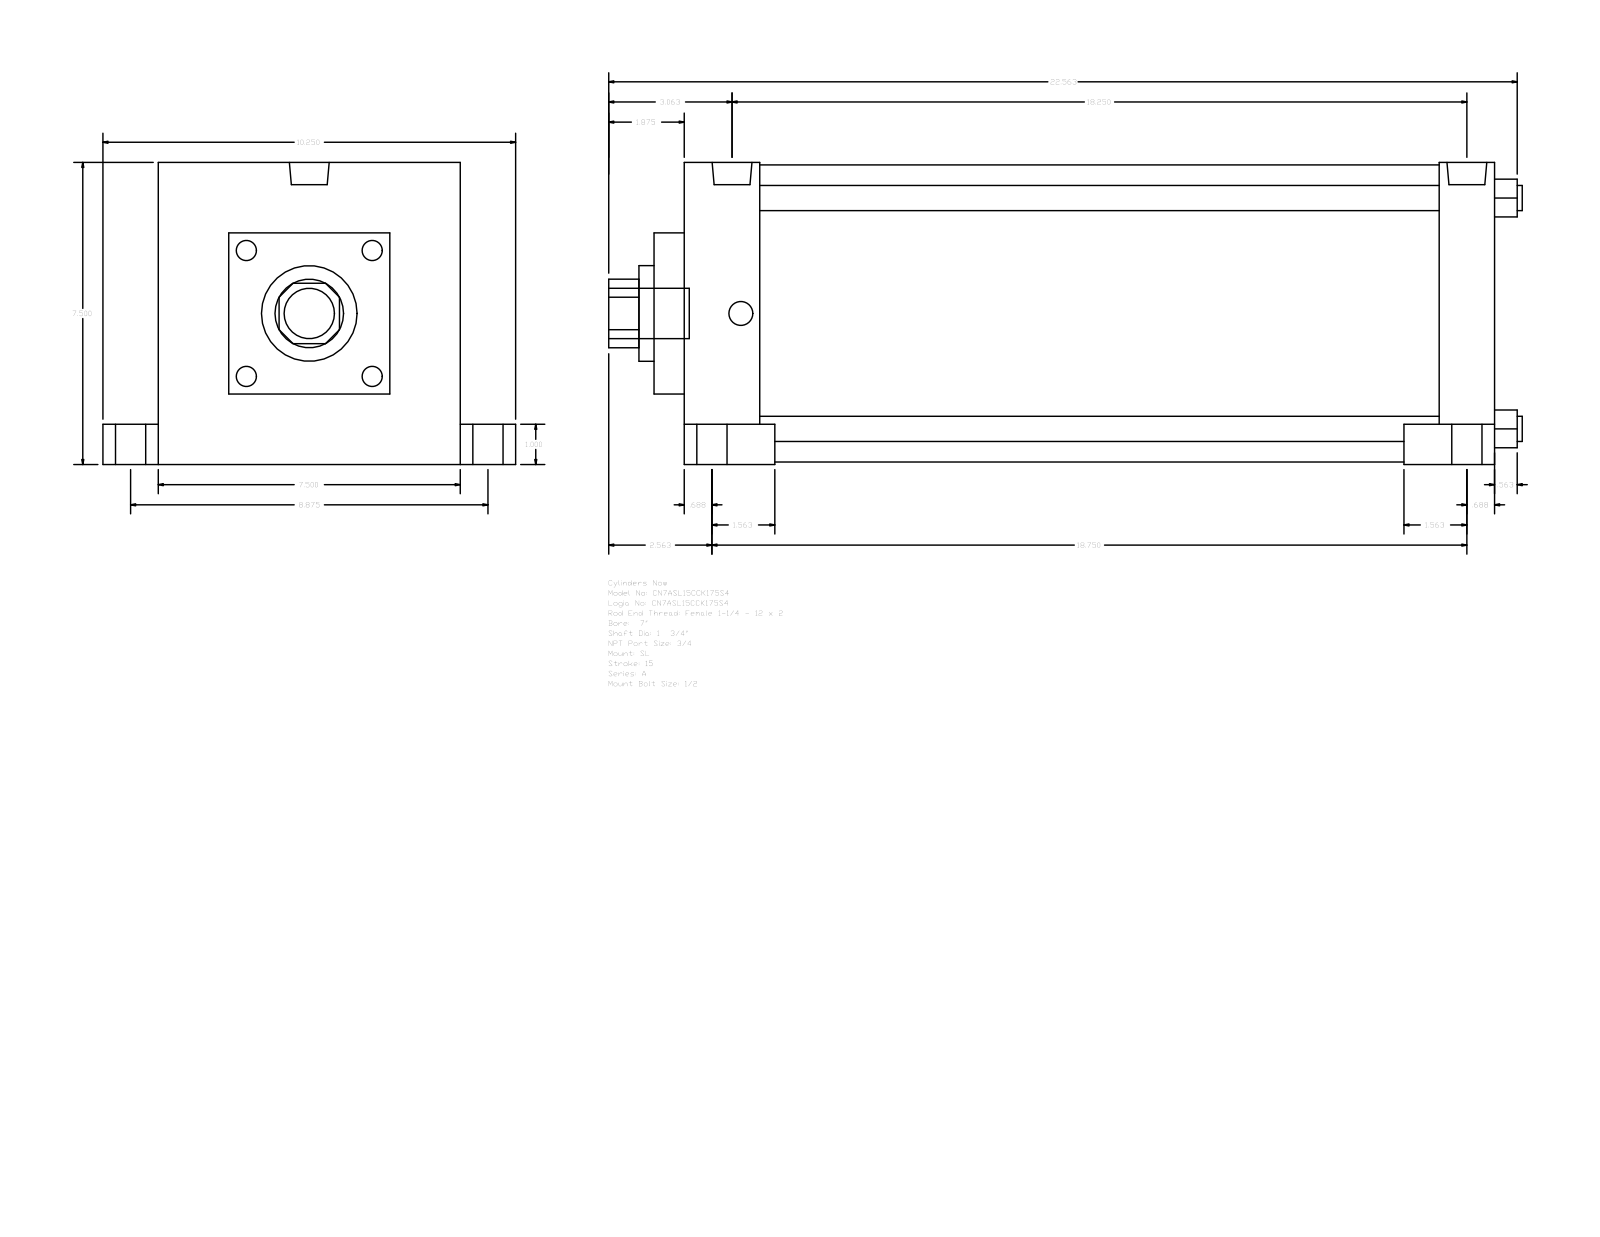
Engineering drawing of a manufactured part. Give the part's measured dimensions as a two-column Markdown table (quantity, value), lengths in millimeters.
| quantity | value |
| --- | --- |
| part name | A_SL__0700_1.75 |
| STEP written by | GSSL Pune (CONFIG_CONTROL_DESIGN) |
| units | millimeters |
| bodies | 0 solids, 117 faces (85 planar, 32 cylindrical, 0 other) |
| overall size | 576.26 × 260.35 × 190.5 |
| round holes (diameter × count) | 15.88 × 4, 44.45 × 1, 60.33 × 1, 187.32 × 1 |
| round bosses / shafts (diameter × count) | 25.4 × 4, 19.05 × 4, 15.08 × 4, 25.12 × 2, 31.75 × 1 |
| partial cylindrical surfaces (radius × count) | 21.63 × 1 |
| main face-to-face distances | 190.5, 511.18, 19.05, 44.45, 34.92, 47.63, 463.55, 476.26, 428.63, 146.05 |
| hole center spacings | 102.91, 145.54, 205.82 |
